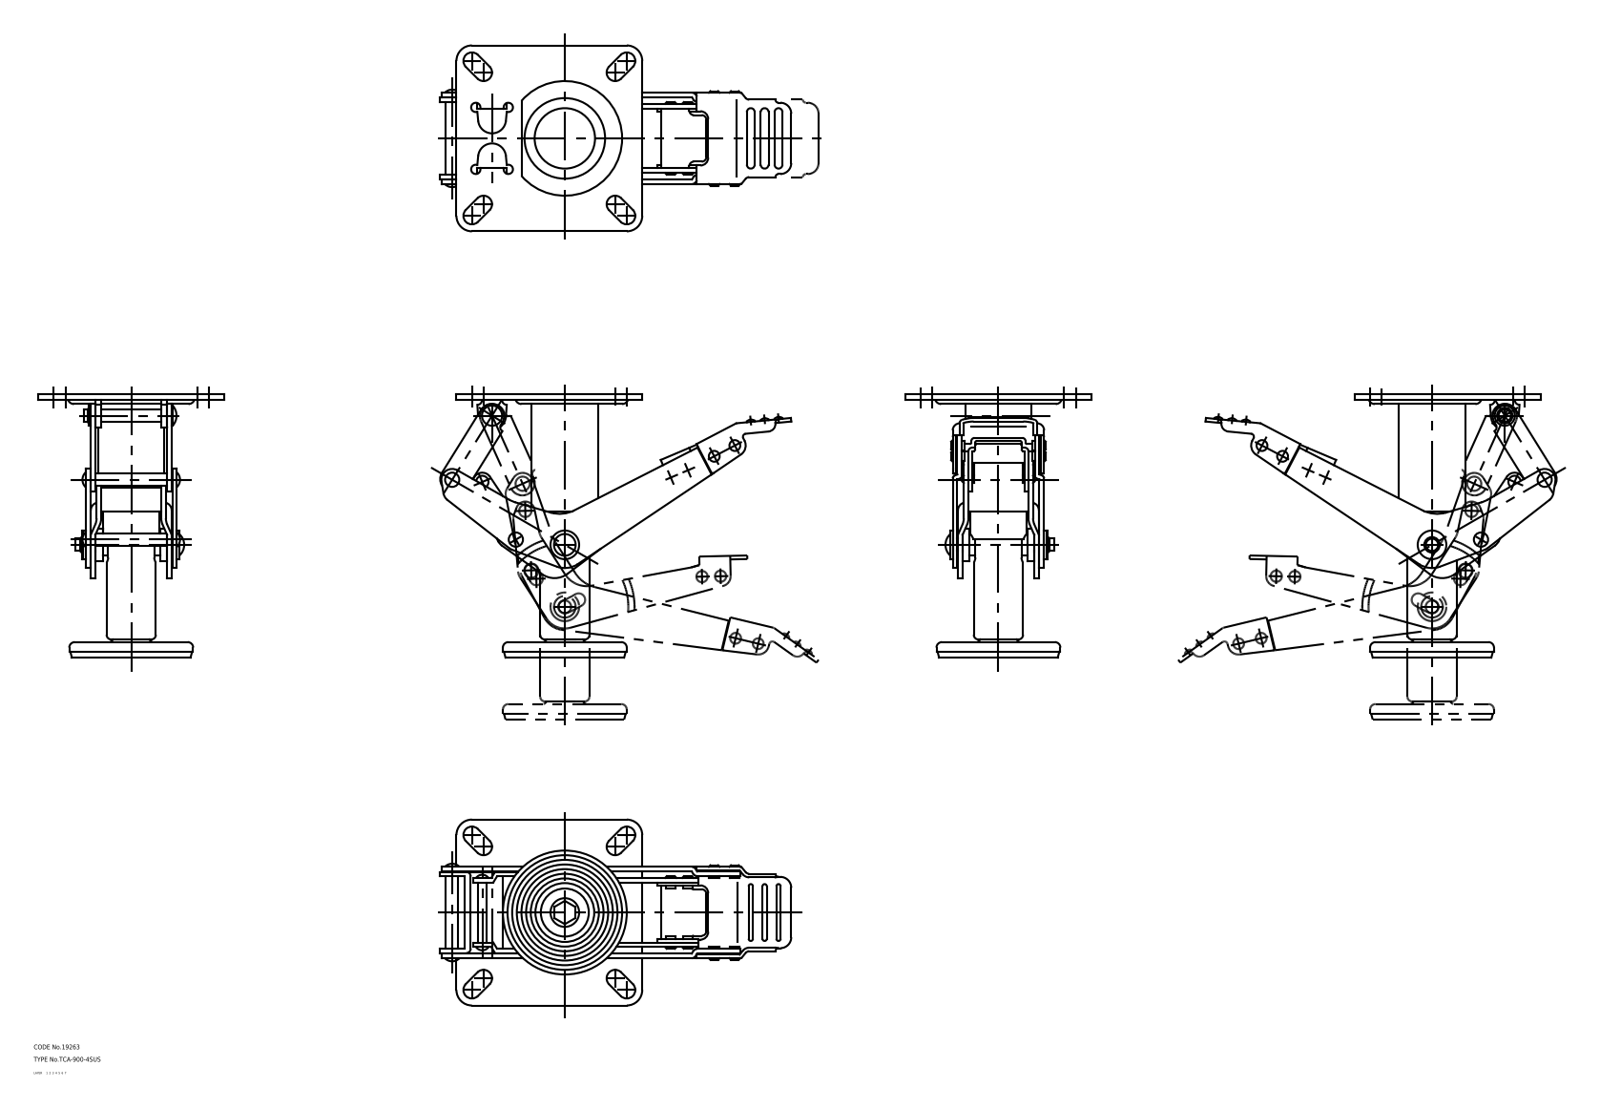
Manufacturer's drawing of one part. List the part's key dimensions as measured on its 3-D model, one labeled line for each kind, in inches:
Part name (STEP PRODUCT): pedal_A; support rod_B; support rod_A; pedal_B (+3 more)
STEP written by: CADfix (AUTOMOTIVE_DESIGN)
Units: inches
Bodies: 6 solids, 545 faces (0 planar, 0 cylindrical, 545 other)
Overall size (bounding box): 8.924 × 6.693 × 4.724
Volume: 16.34 in³ · Surface area: 266.6 in²
